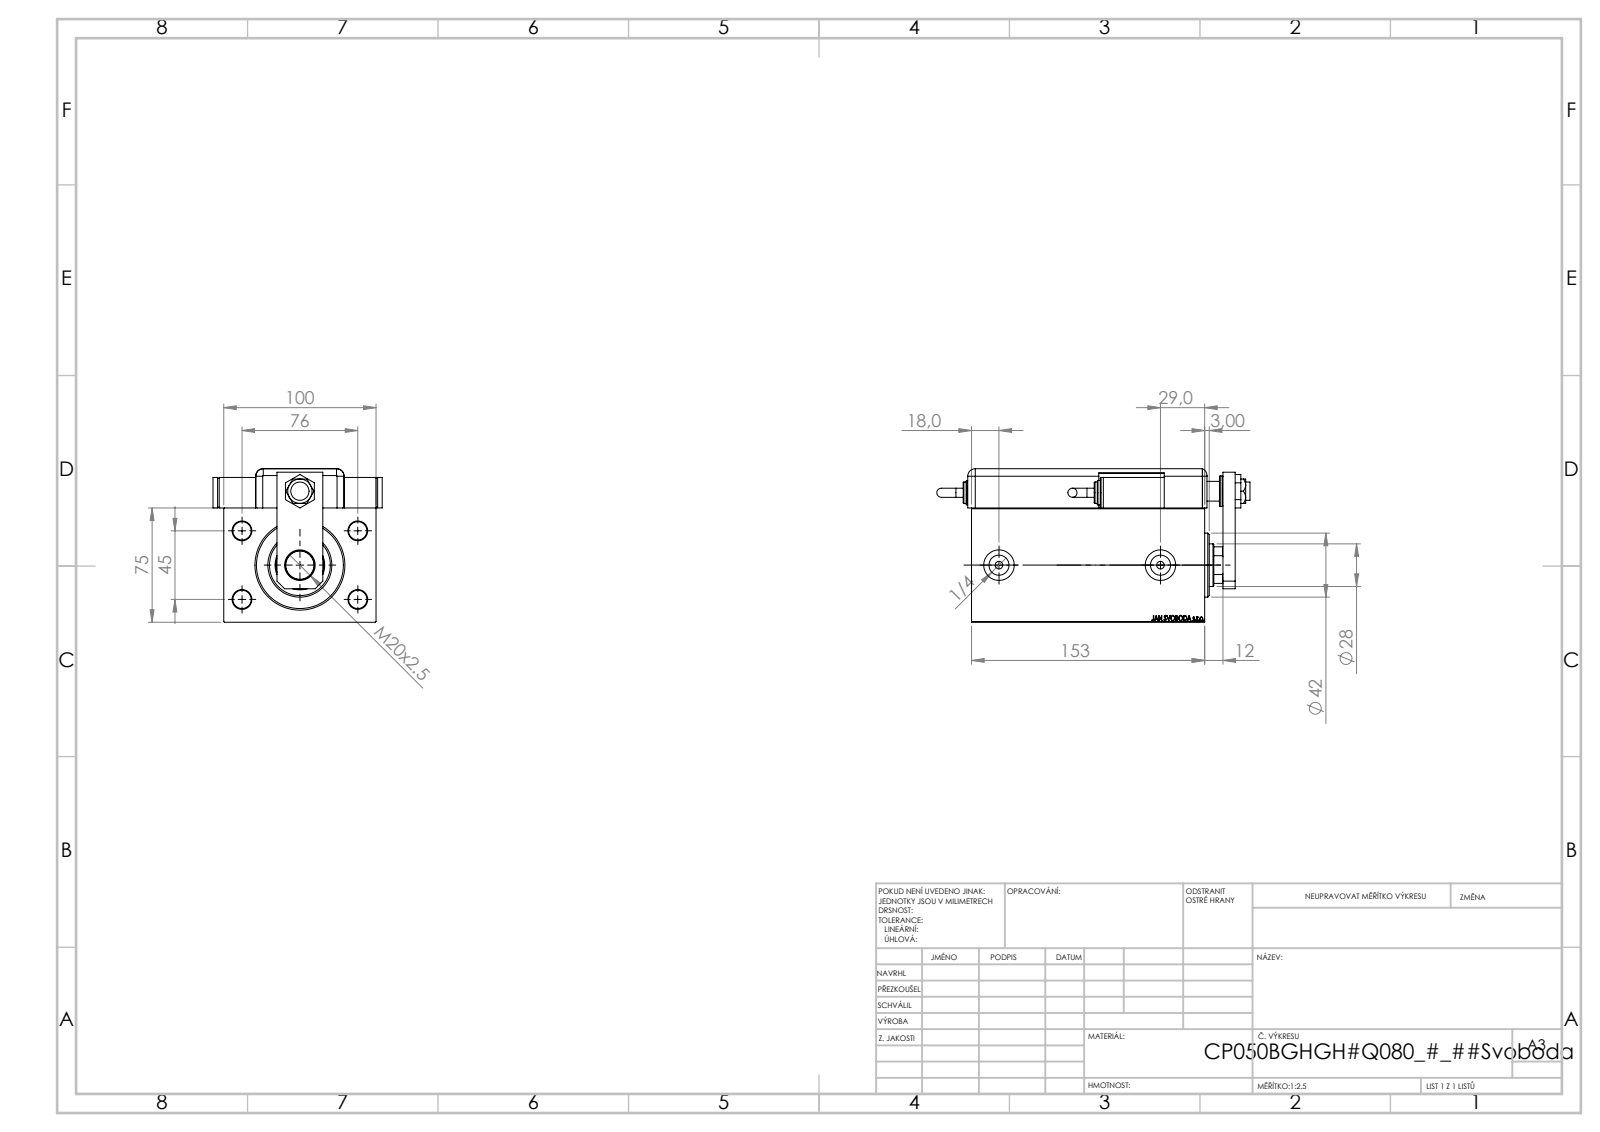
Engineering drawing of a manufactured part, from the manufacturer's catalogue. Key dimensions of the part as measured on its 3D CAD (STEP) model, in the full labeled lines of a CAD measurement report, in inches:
Part name (STEP PRODUCT): V450CM_B_Body; NUT_D19; MAGNETIC SWITCH Q; V450CM_B_VCP (+7 more)
STEP written by: SolidWorks 2019 (CONFIG_CONTROL_DESIGN)
Units: inches
Bodies: 13 solids, 1268 faces (608 planar, 111 cylindrical, 549 other)
Overall size (bounding box): 8.089 × 4.37 × 3.969
Volume: 72.31 in³ · Surface area: 302.6 in²
Round holes (diameter × count): ⌀0.472 ×5, ⌀0.787 ×3, ⌀0.157 ×2, ⌀0.197 ×2, ⌀0.315 ×2, ⌀0.518 ×2, ⌀0.512 ×1, ⌀0.551 ×1, ⌀0.728 ×1, ⌀1.102 ×1, ⌀1.24 ×1, ⌀1.28 ×1
Round bosses / shafts (diameter × count): ⌀0.787 ×3, ⌀0.63 ×2, ⌀0.551 ×2, ⌀0.236 ×2, ⌀1.654 ×1
Partial cylindrical surfaces — rounded edges, fillets, slot ends (radius × count): R0.197 ×9, R0.394 ×1, R0.531 ×1
Main face-to-face distances: 2.953, 0.118, 3.937, 1.016, 3.969, 0.945, 0.551, 3.85, 0.898, 6.024
Hole centre spacings: 1.739, 1.772, 1.813, 2.992, 3.17, 3.477, 0.787, 1.909
